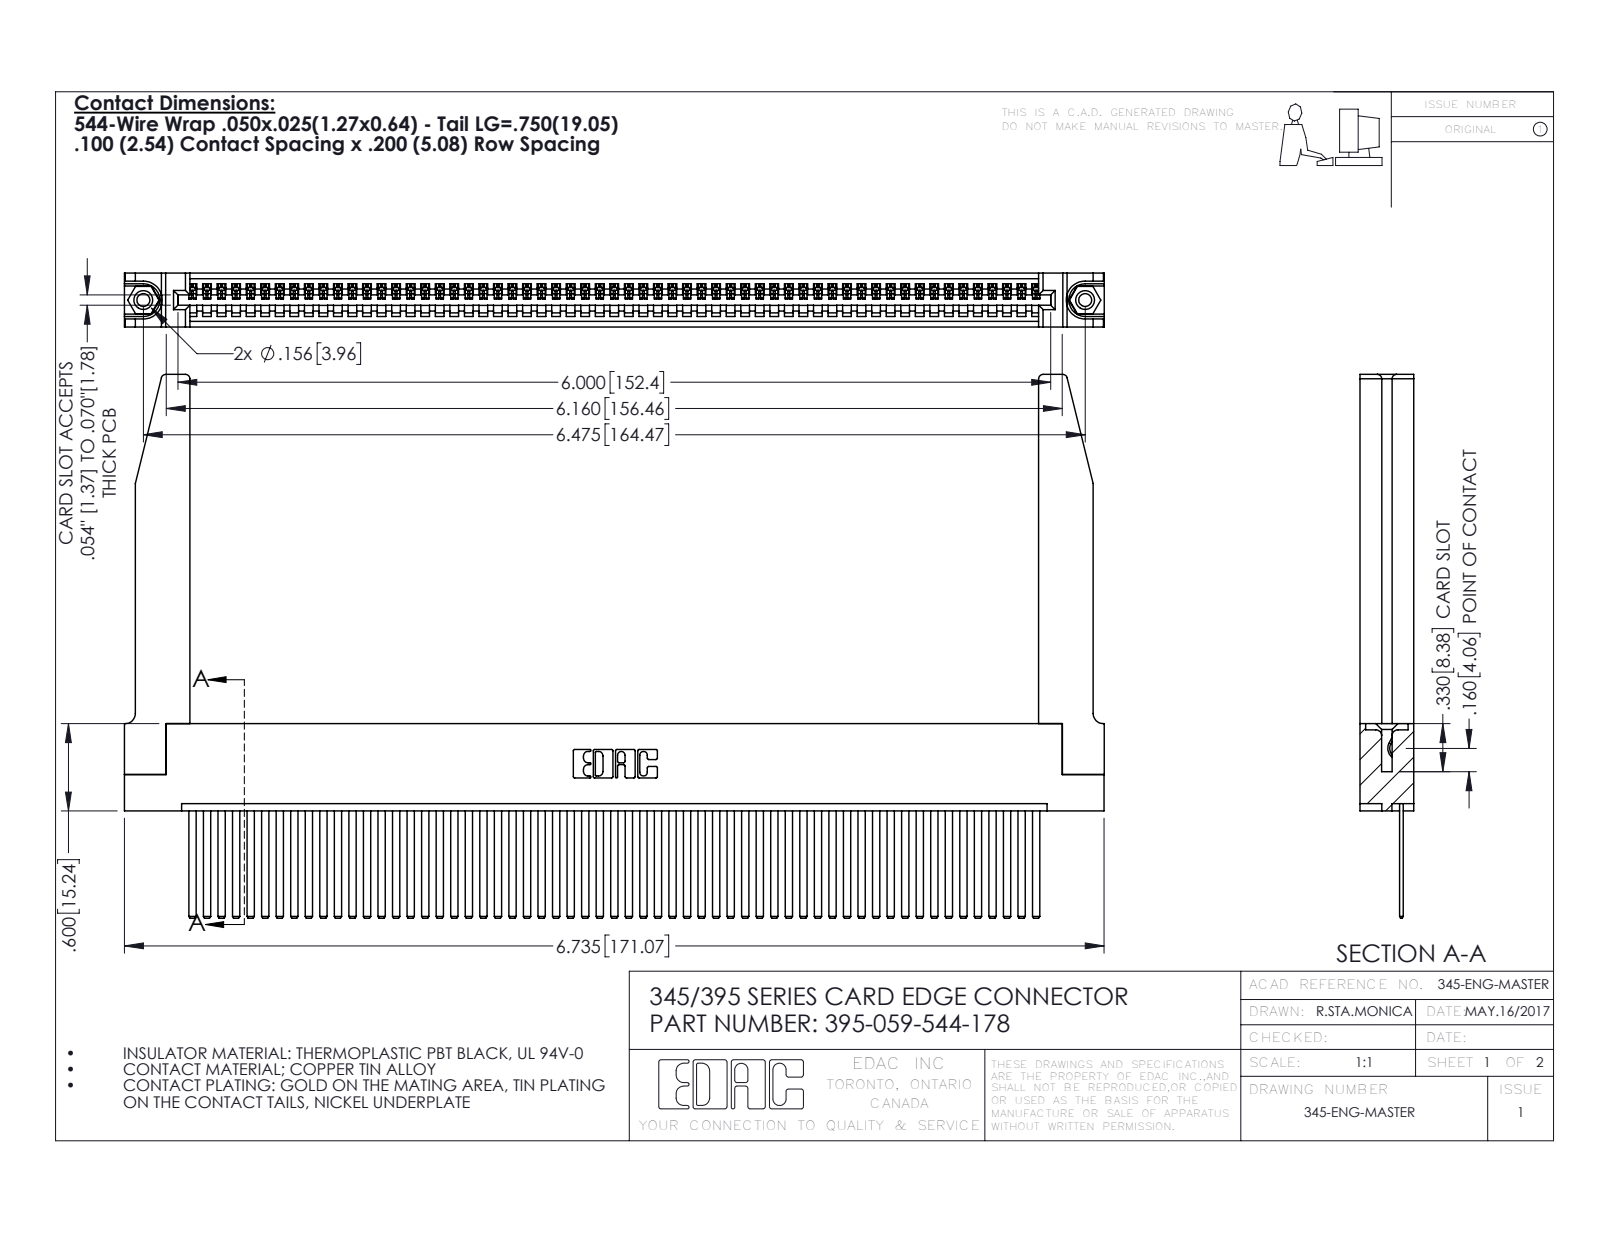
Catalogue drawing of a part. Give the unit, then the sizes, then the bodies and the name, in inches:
Units: inches
Overall size (bounding box): 6.736 × 3.737 × 0.37
Round holes (diameter × count): ⌀0.089 ×2, ⌀0.125 ×2, ⌀0.156 ×2, ⌀0.064 ×1
Round bosses / shafts (diameter × count): ⌀0.155 ×2
Partial cylindrical surfaces — rounded edges, fillets, slot ends (radius × count): R0.006 ×118, R0.01 ×22, R0.03 ×8, R0.007 ×6, R0.031 ×6, R0.026 ×3, R0.031 ×2, R0.04 ×2
Main face-to-face distances: 0.072, 0.298, 0.37, 0.098, 0.272, 0.025, 0.2, 0.225, 0.148, 0.15
Hole centre spacings: 0.27, 6.239, 6.475
Volume: 1.516 in³ · Surface area: 49.32 in²
Bodies: 64 solids, 3428 faces (2346 planar, 1030 cylindrical, 52 other)
Part name (STEP PRODUCT): 345-292-001_345-293-144; 345-220-078_345-220-078; 345 Part_Flush Mounting Lugs - 0.156 Dia-TH; 345-250-001_345-250-001-102 (+1 more)
STEP written by: SolidWorks 2016 (CONFIG_CONTROL_DESIGN)
